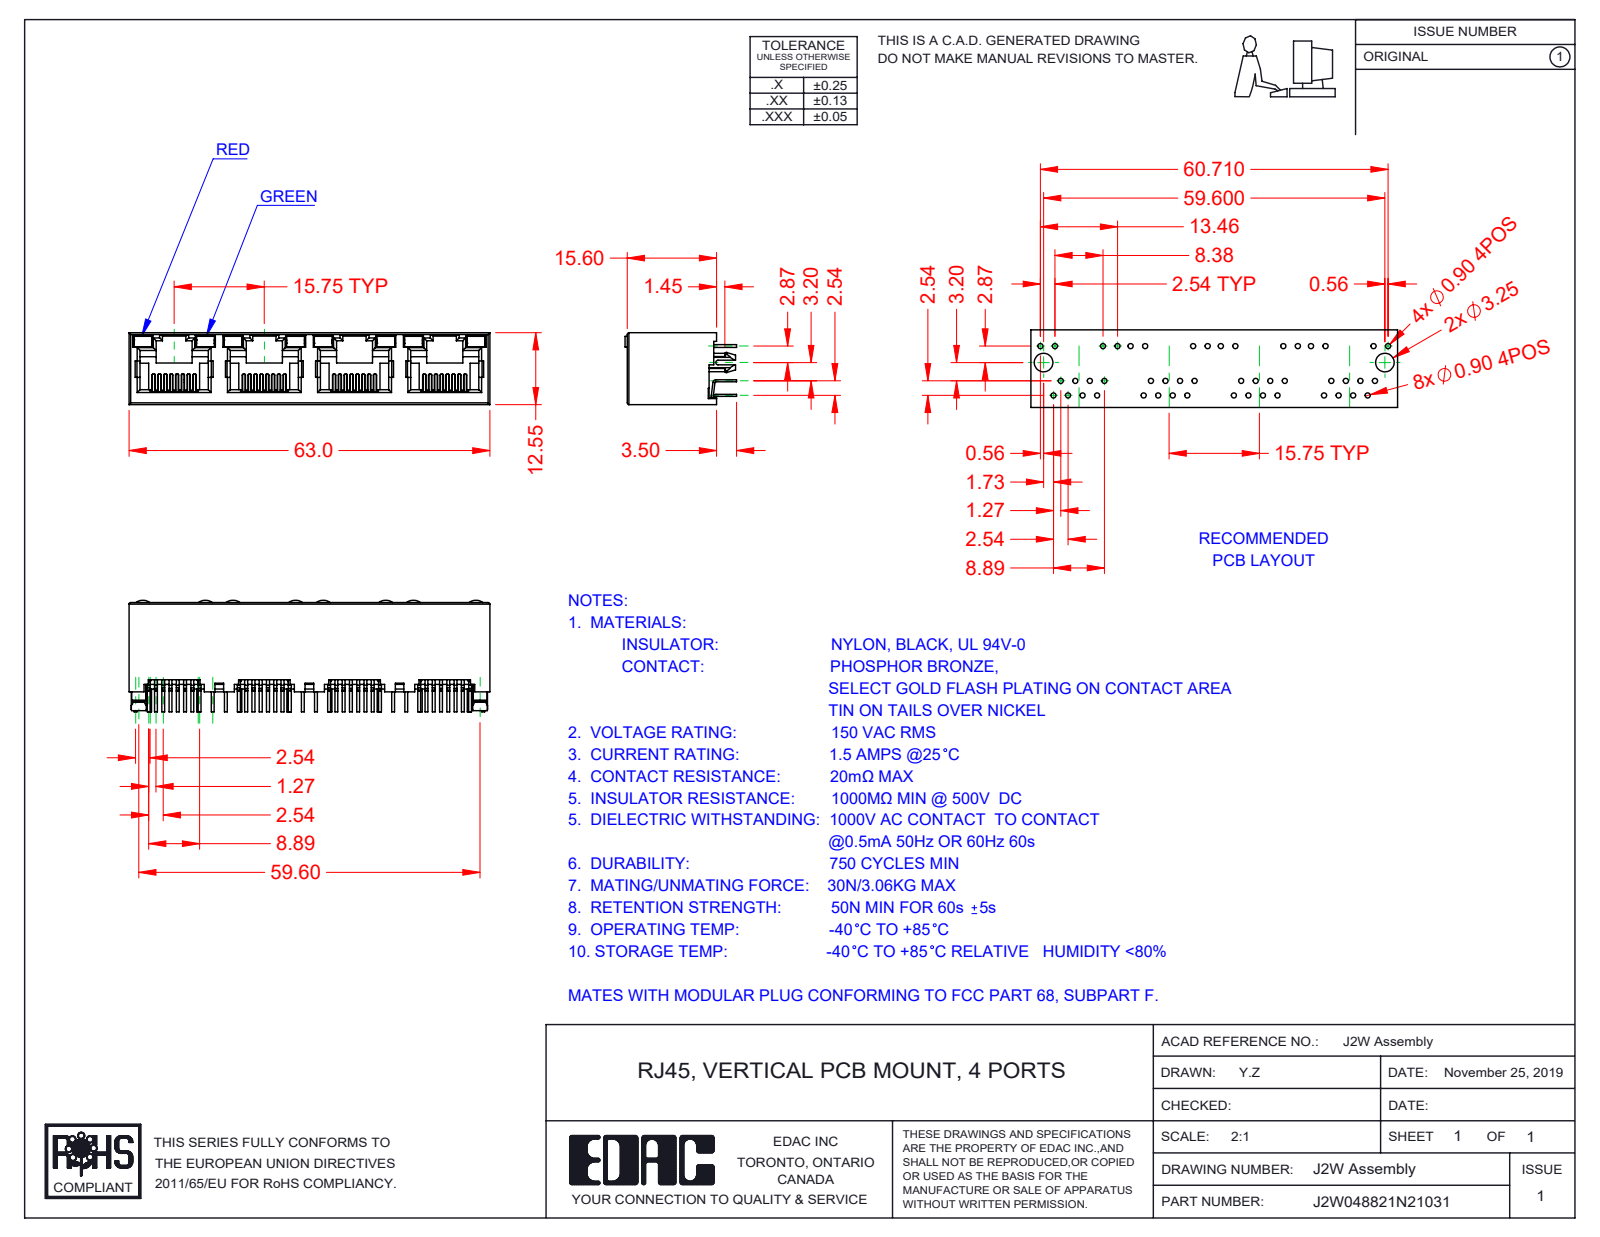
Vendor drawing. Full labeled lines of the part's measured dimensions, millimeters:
Part name (STEP PRODUCT): 2W Contact Lock; 2W Contacts; 2W LED LH_2-Red; 2W Insulator (+2 more)
STEP written by: SolidWorks 2016 (CONFIG_CONTROL_DESIGN)
Units: millimetres
Bodies: 45 solids, 3135 faces (2600 planar, 477 cylindrical, 58 other)
Overall size (bounding box): 63 × 19.5 × 12.55
Volume: 5 335 mm³ · Surface area: 13 144 mm²
Partial cylindrical surfaces — rounded edges, fillets, slot ends (radius × count): R0.15 ×64, R0.2 ×29, R0.5 ×28, R0.3 ×14, R0.45 ×8, R2 ×8, R0.25 ×2, R1.5 ×2
Main face-to-face distances: 12.55, 11.9, 0.65, 15.75, 0.36, 1.5, 0.78, 0.6, 11.3, 31.5
